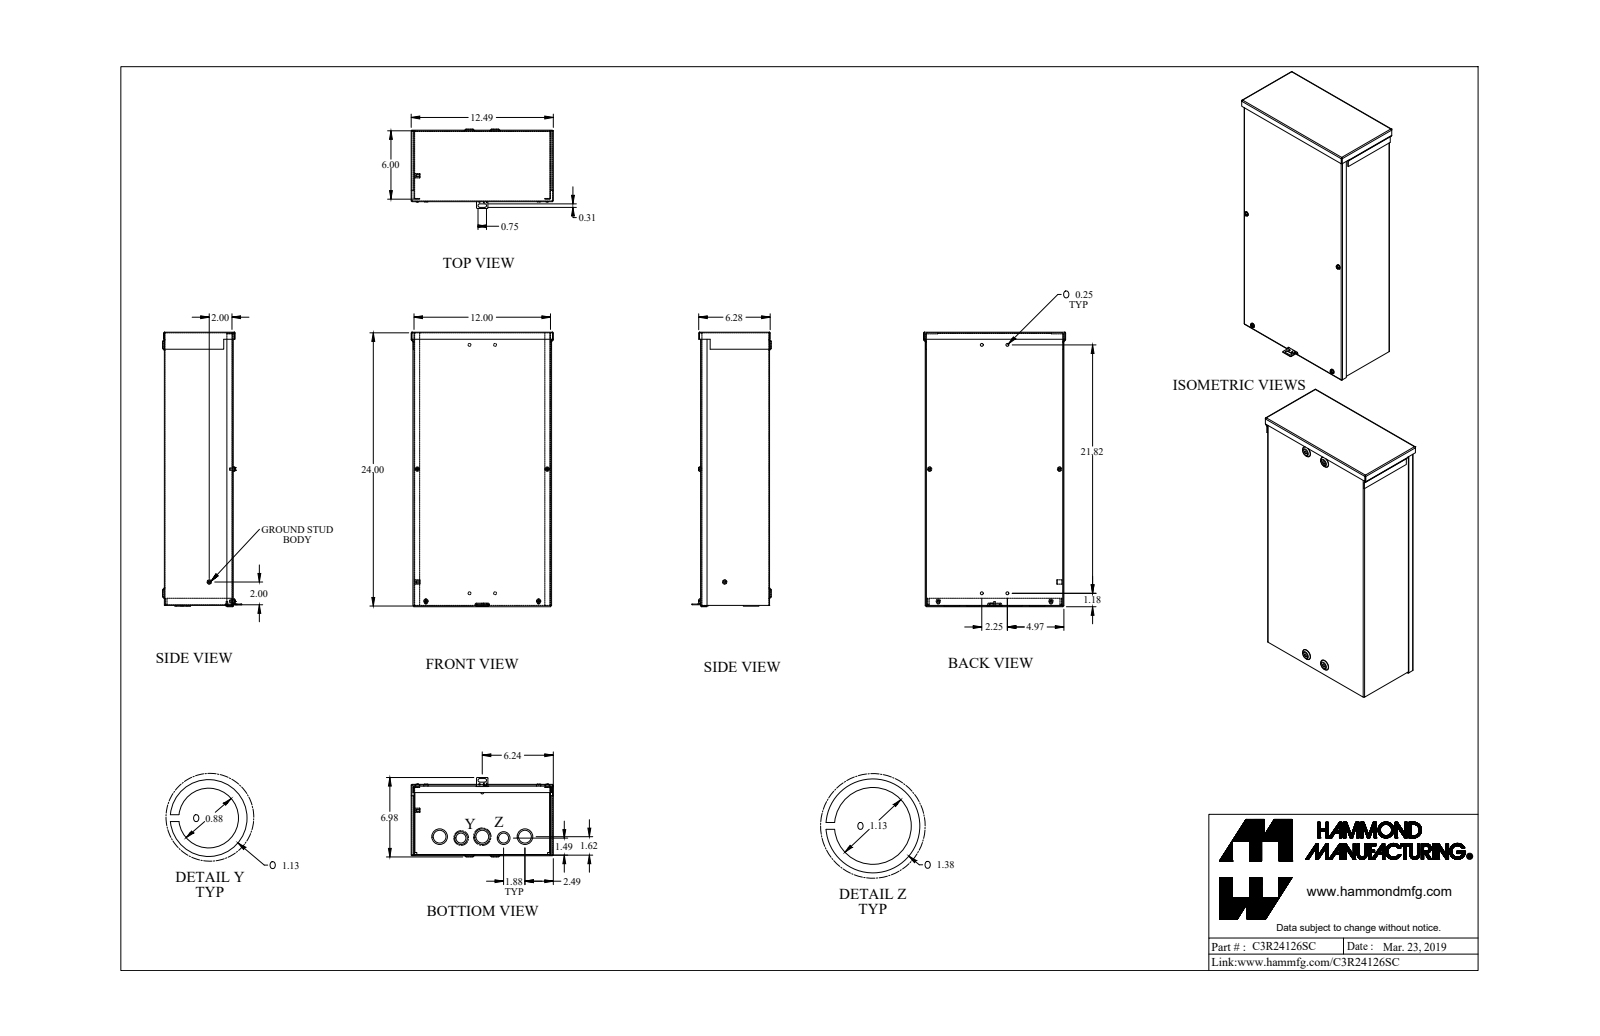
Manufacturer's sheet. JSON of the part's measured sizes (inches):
{"part_name": "C3R24126SC_Default", "step_written_by": "SolidWorks 2019 (CONFIG_CONTROL_DESIGN)", "units": "inches", "bodies": {"solids": 11, "faces": 429, "planar": 226, "cylindrical": 117, "other": 86}, "overall_size": [24.12, 12.489, 6.977], "volume_in3": 63.76, "surface_area_in2": 2249, "round_holes": [[0.17, 4], [0.25, 4], [1.125, 3], [0.875, 2], [0.125, 1], [0.137, 1], [0.156, 1]], "round_bosses_or_shafts": [[0.19, 4], [0.375, 3], [1.375, 2], [1.125, 2], [0.375, 2], [1.375, 1], [0.125, 1]], "partial_cylinders_radius": [[0.029, 21], [0.086, 21], [0.109, 8], [0.125, 8], [0.156, 2]], "face_to_face_distances": [0.057, 6, 5.943, 6.057, 11.943, 12, 11.886, 0.057, 23.886, 23.943], "hole_center_spacings": [11.832, 12.872, 3.75, 1.879, 1.88, 2.25, 3.92, 5.396]}
